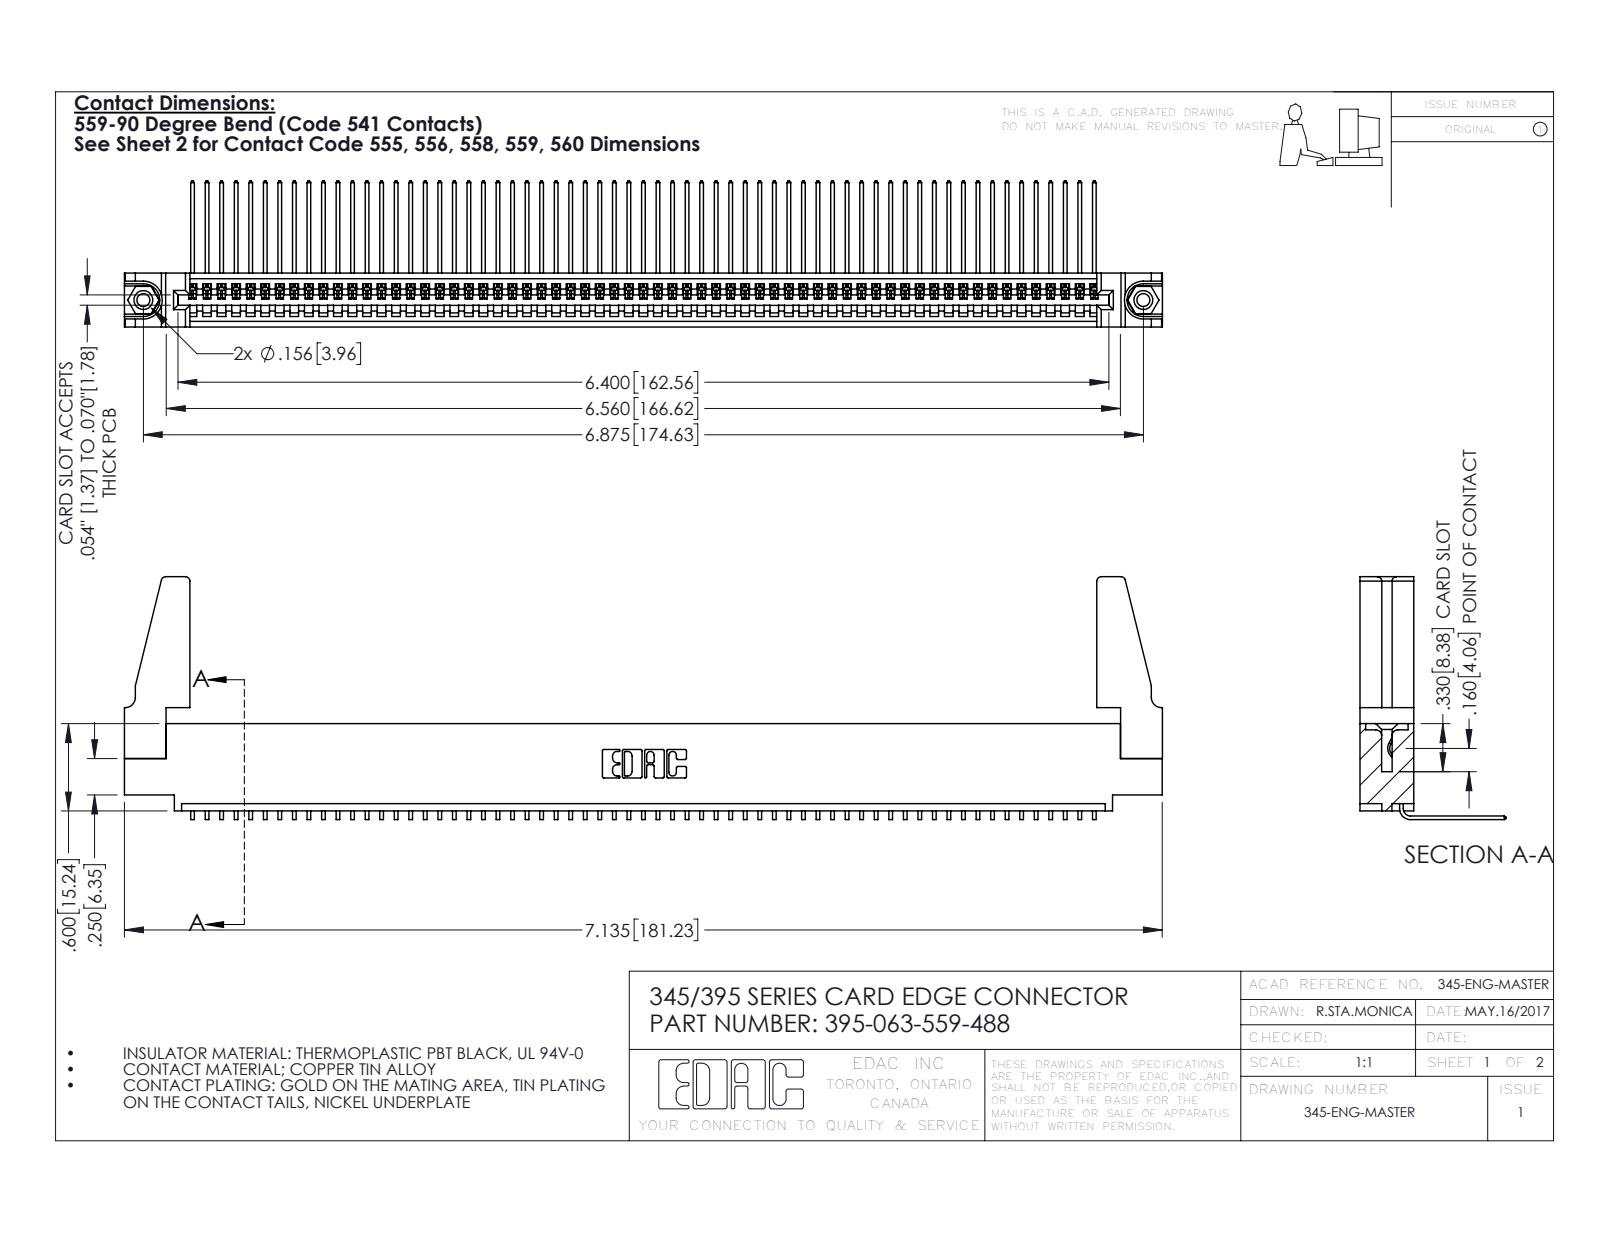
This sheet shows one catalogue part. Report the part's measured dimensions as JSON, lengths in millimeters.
{"part_name": "395-063-559-488; 345-292-001_558 559 Tail - 1; 345 Part_0.110 Offset - 0.156 Dia-TH; 345-220-078_345-220-088 (+1 more)", "step_written_by": "SolidWorks 2016 (CONFIG_CONTROL_DESIGN)", "units": "millimeters", "bodies": {"solids": 68, "faces": 4034, "planar": 2802, "cylindrical": 1216, "other": 16}, "overall_size": [181.3, 42.4, 25.5], "volume_mm3": 20780, "surface_area_mm2": 28020, "round_holes": [[2.3, 2], [3.2, 2], [4, 2], [1.6, 1]], "round_bosses_or_shafts": [[3.9, 2]], "partial_cylinders_radius": [[0.2, 126], [0.3, 22], [0.8, 8], [0.2, 6], [0.8, 6], [0.7, 3], [0.8, 2], [1, 2]], "face_to_face_distances": [1.8, 7.6, 9.4, 5.1, 2.5, 6.9, 0.6, 5.7, 3.8, 1.8], "hole_center_spacings": [6.9, 168.6, 174.6]}
